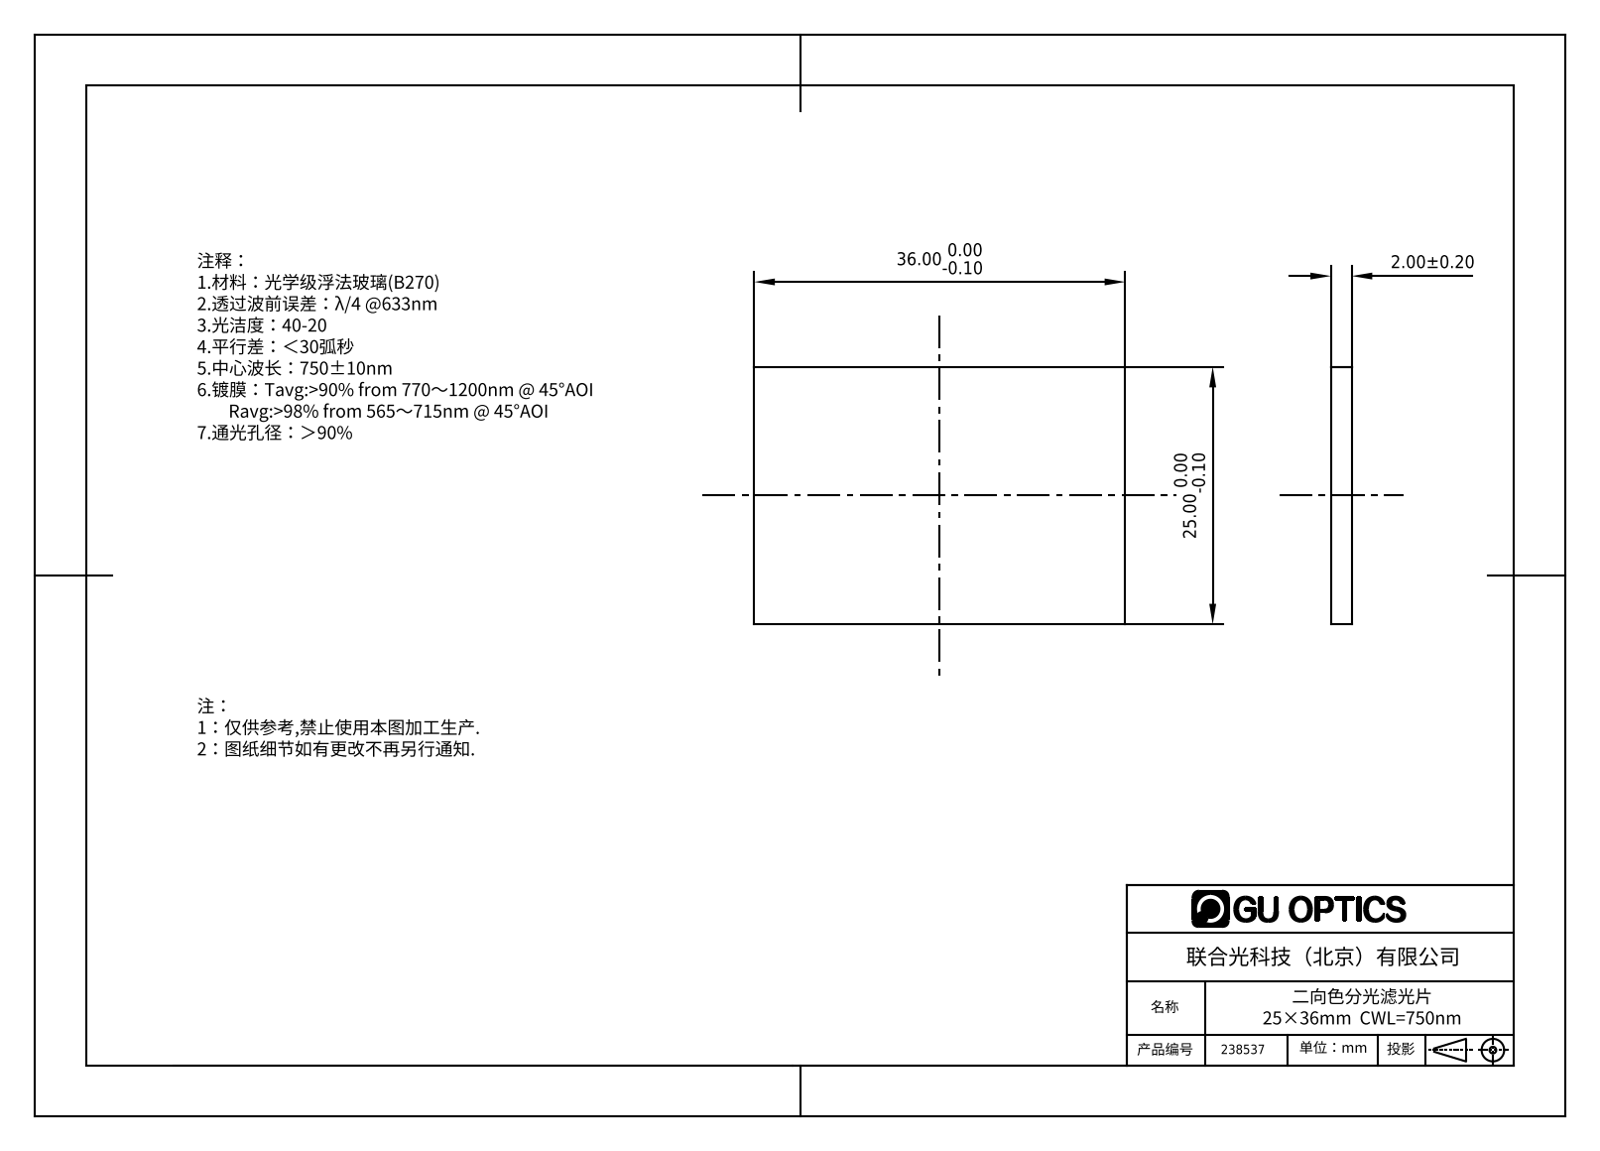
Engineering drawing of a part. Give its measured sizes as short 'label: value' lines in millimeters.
name: 238530
written by: SolidWorks 2016 (AUTOMOTIVE_DESIGN)
unit: mm
bodies: 1 solid, 6 faces (6 planar, 0 cylindrical, 0 other)
size: 36 × 25 × 2
volume: 1 800 mm³; area: 2 044 mm²
face distances: 2, 25, 36
